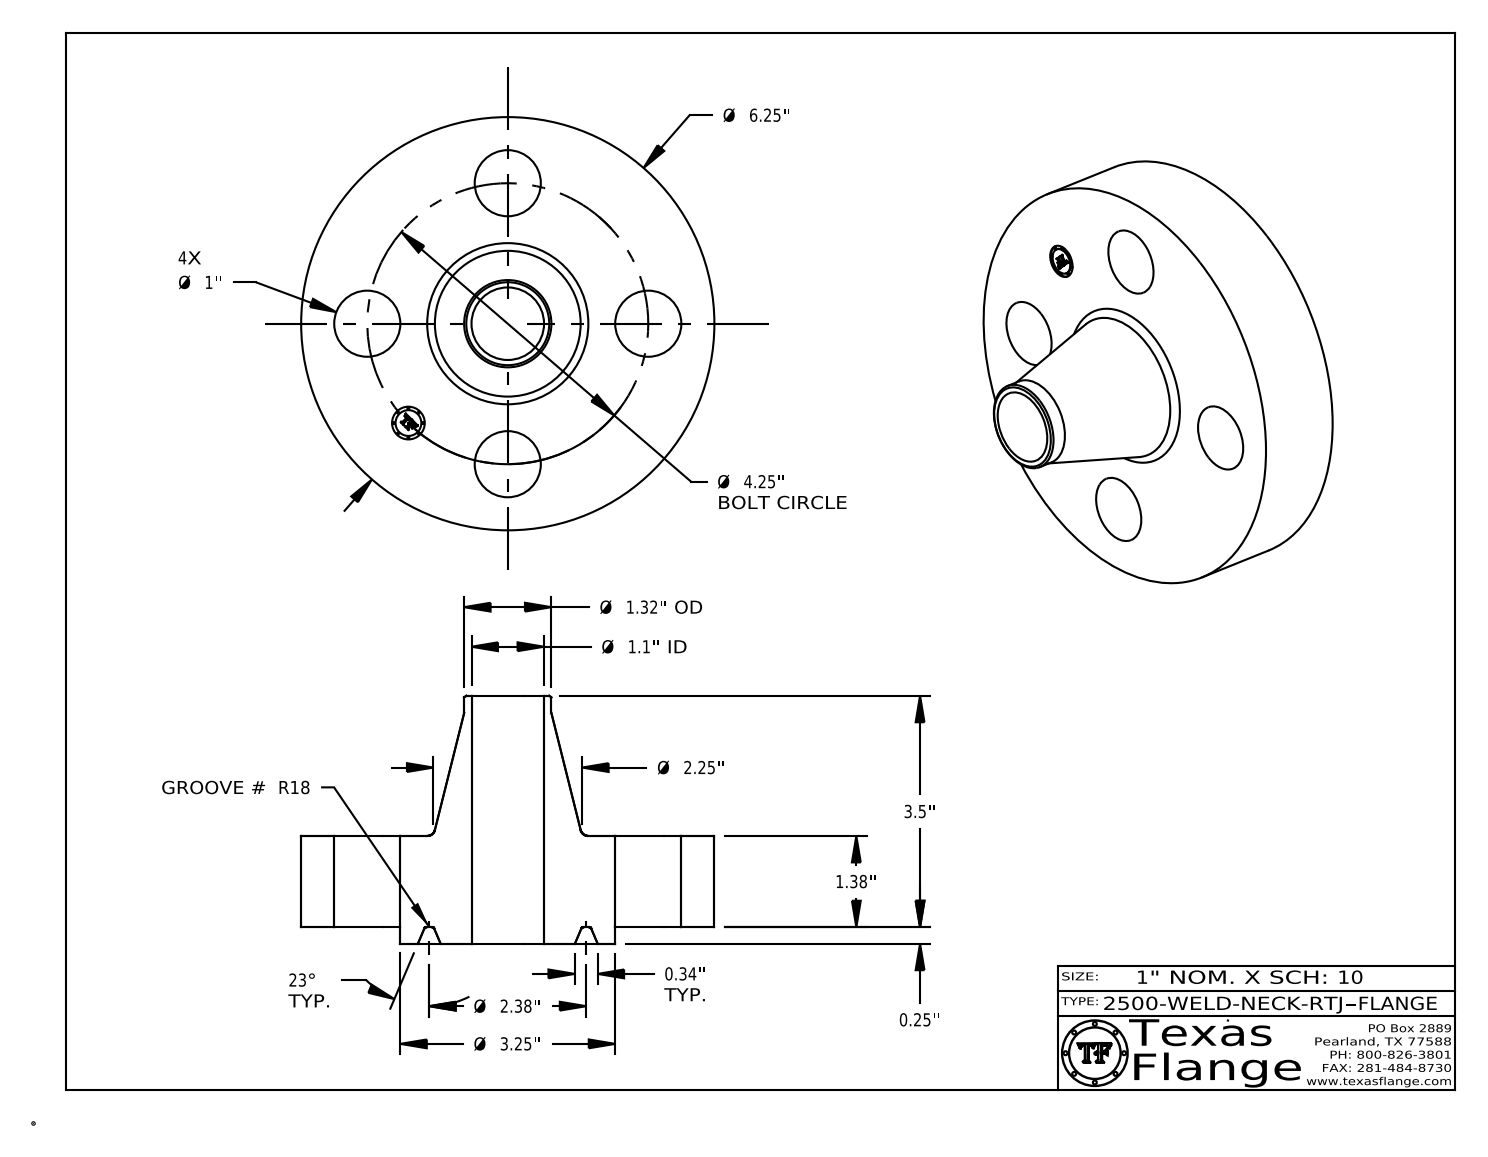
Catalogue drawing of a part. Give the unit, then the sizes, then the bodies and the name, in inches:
Units: inches
Overall size (bounding box): 6.25 × 6.25 × 3.75
Round holes (diameter × count): ⌀1 ×4, ⌀0.495 ×1, ⌀1.097 ×1
Round bosses / shafts (diameter × count): ⌀0.03 ×8, ⌀6.25 ×1, ⌀3.25 ×1, ⌀1.32 ×1, ⌀0.39 ×1
Main face-to-face distances: 1.38, 0.25, 1.63, 3.75, 3.5, 2.12, 1.615, 1.365, 0.015, 2.135
Hole centre spacings: 2.125, 3.006, 1.626, 3.927, 4.25
Volume: 41.21 in³ · Surface area: 124.5 in²
Bodies: 1 solid, 421 faces (371 planar, 36 cylindrical, 14 other)
Part name (STEP PRODUCT): 2500-WELD-NECK-RTJ
STEP written by: CATIA V5 STEP AP214 (AUTOMOTIVE_DESIGN)
